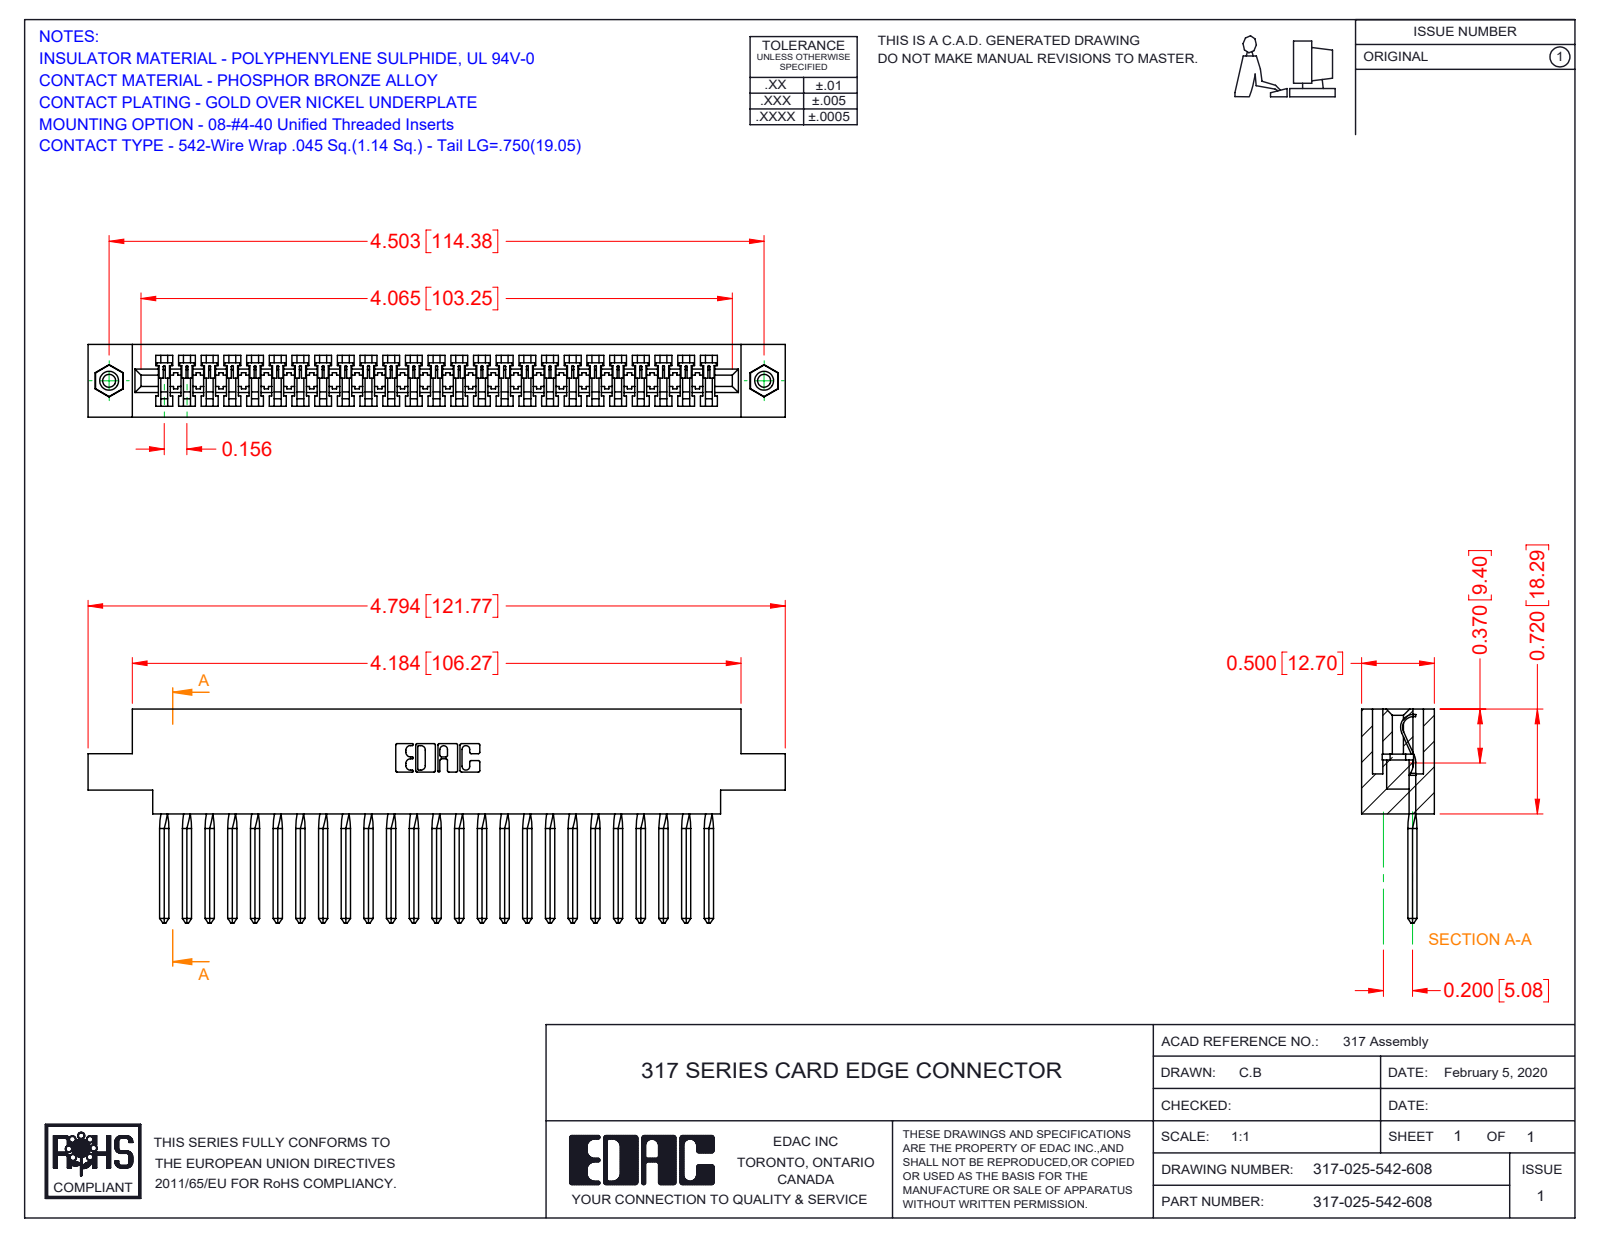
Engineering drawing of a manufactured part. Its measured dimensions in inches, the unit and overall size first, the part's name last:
Units: inches
Overall size (bounding box): 4.794 × 1.47 × 0.5
Round holes (diameter × count): ⌀0.089 ×2, ⌀0.125 ×2, ⌀0.156 ×2
Round bosses / shafts (diameter × count): ⌀0.155 ×2
Partial cylindrical surfaces — rounded edges, fillets, slot ends (radius × count): R0.006 ×50, R0.01 ×22, R0.007 ×6, R0.031 ×6, R0.026 ×3, R0.074 ×1, R0.089 ×1, R0.1 ×1
Main face-to-face distances: 0.5, 0.075, 0.425, 0.35, 0.11, 0.136, 0.72, 0.211, 0.289, 0.213
Hole centre spacings: 4.503
Volume: 1.12 in³ · Surface area: 34.14 in²
Bodies: 28 solids, 2037 faces (1690 planar, 231 cylindrical, 116 other)
Part name (STEP PRODUCT): 317-025-542-608; 317-290-003_542; 317 Part_.156 Dia - TI; 345-250-001_345-250-003-102
STEP written by: SolidWorks 2016 (CONFIG_CONTROL_DESIGN)
